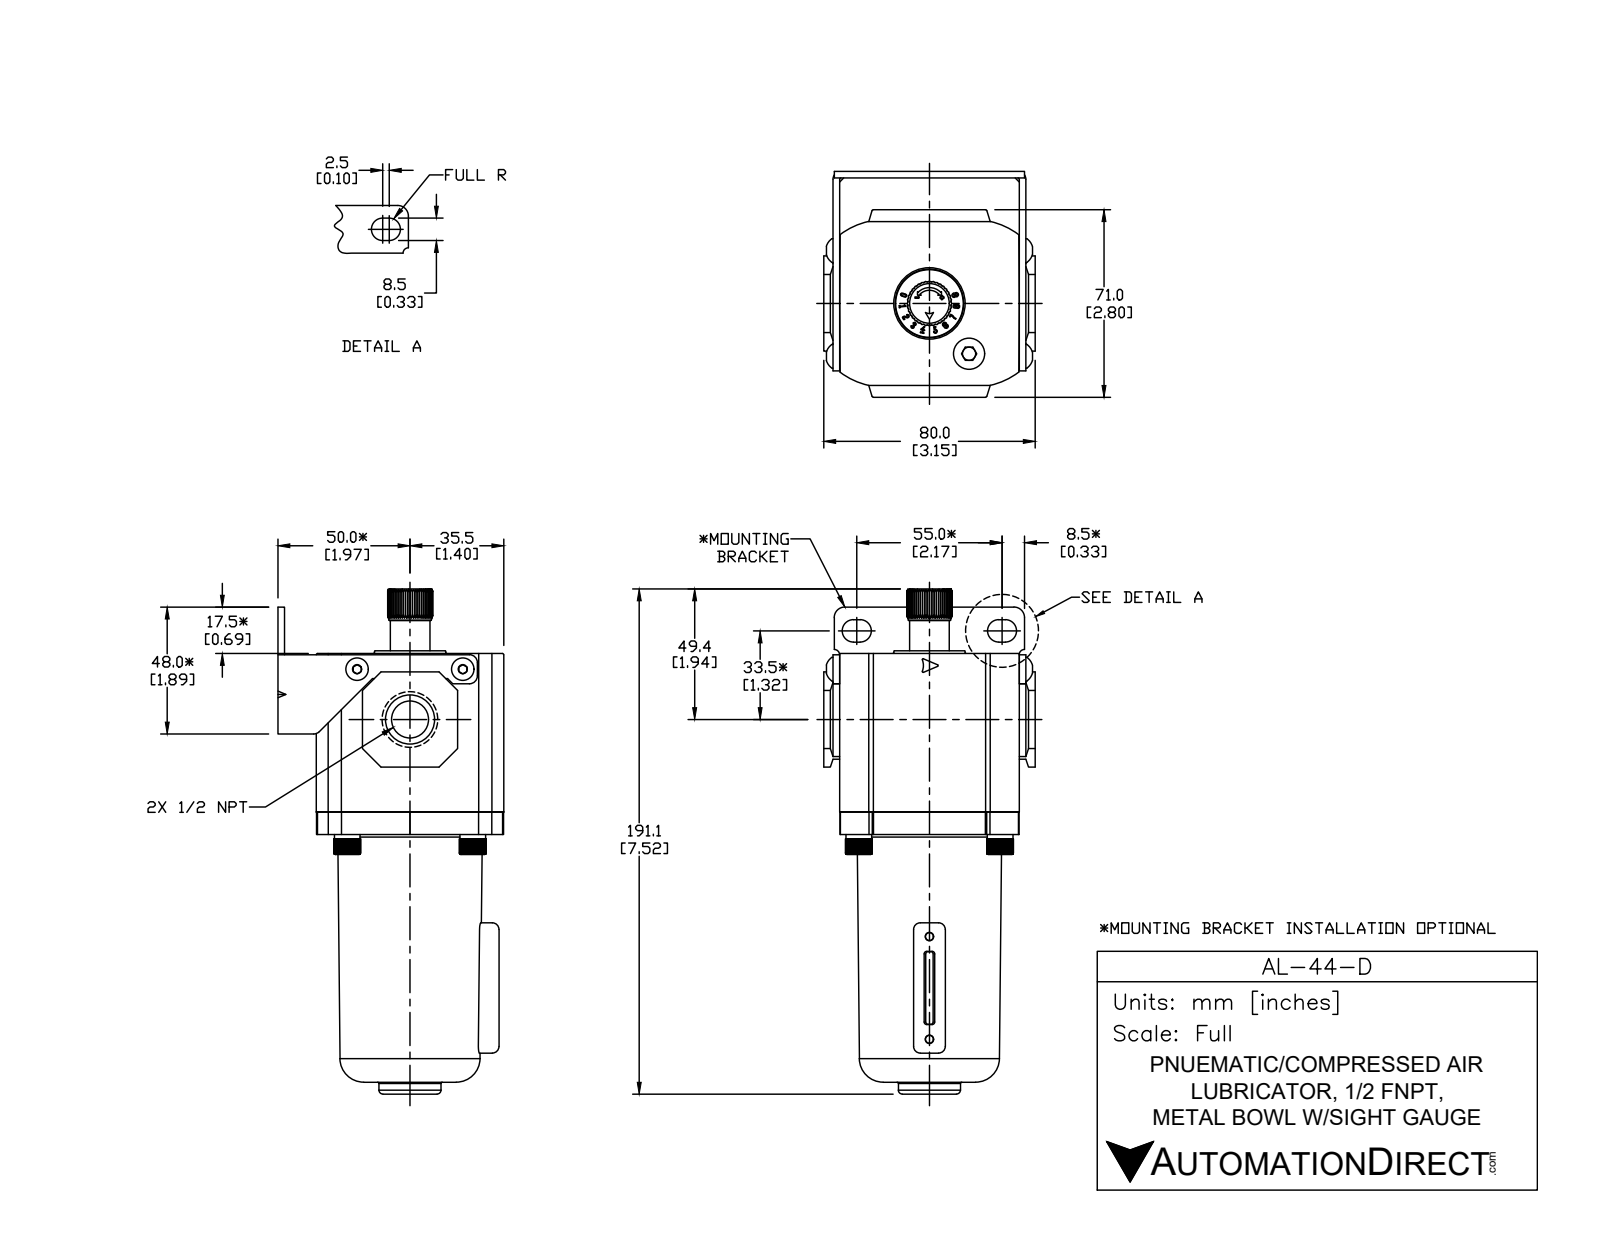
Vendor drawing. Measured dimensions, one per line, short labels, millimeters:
name: AL-44-D
written by: SolidWorks 2015 (CONFIG_CONTROL_DESIGN)
unit: mm
bodies: 7 solids, 575 faces (335 planar, 110 cylindrical, 130 other)
size: 189.73 × 85.7 × 80
volume: 542 916 mm³; area: 72 286 mm²
holes: 2× ⌀3.4, 1× ⌀17.86
bosses: 4× ⌀10, 2× ⌀5.5, 1× ⌀26, 1× ⌀23.5, 1× ⌀15
rounds: 8× R1.3, 8× R2.5, 5× R2, 4× R0.3, 4× R1, 4× R4.25, 4× R17.9, 4× R20
face distances: 2.5, 60, 14.5, 12, 83, 71, 68, 85.5, 70.5, 8.5
hole spacings: 27.59, 40
